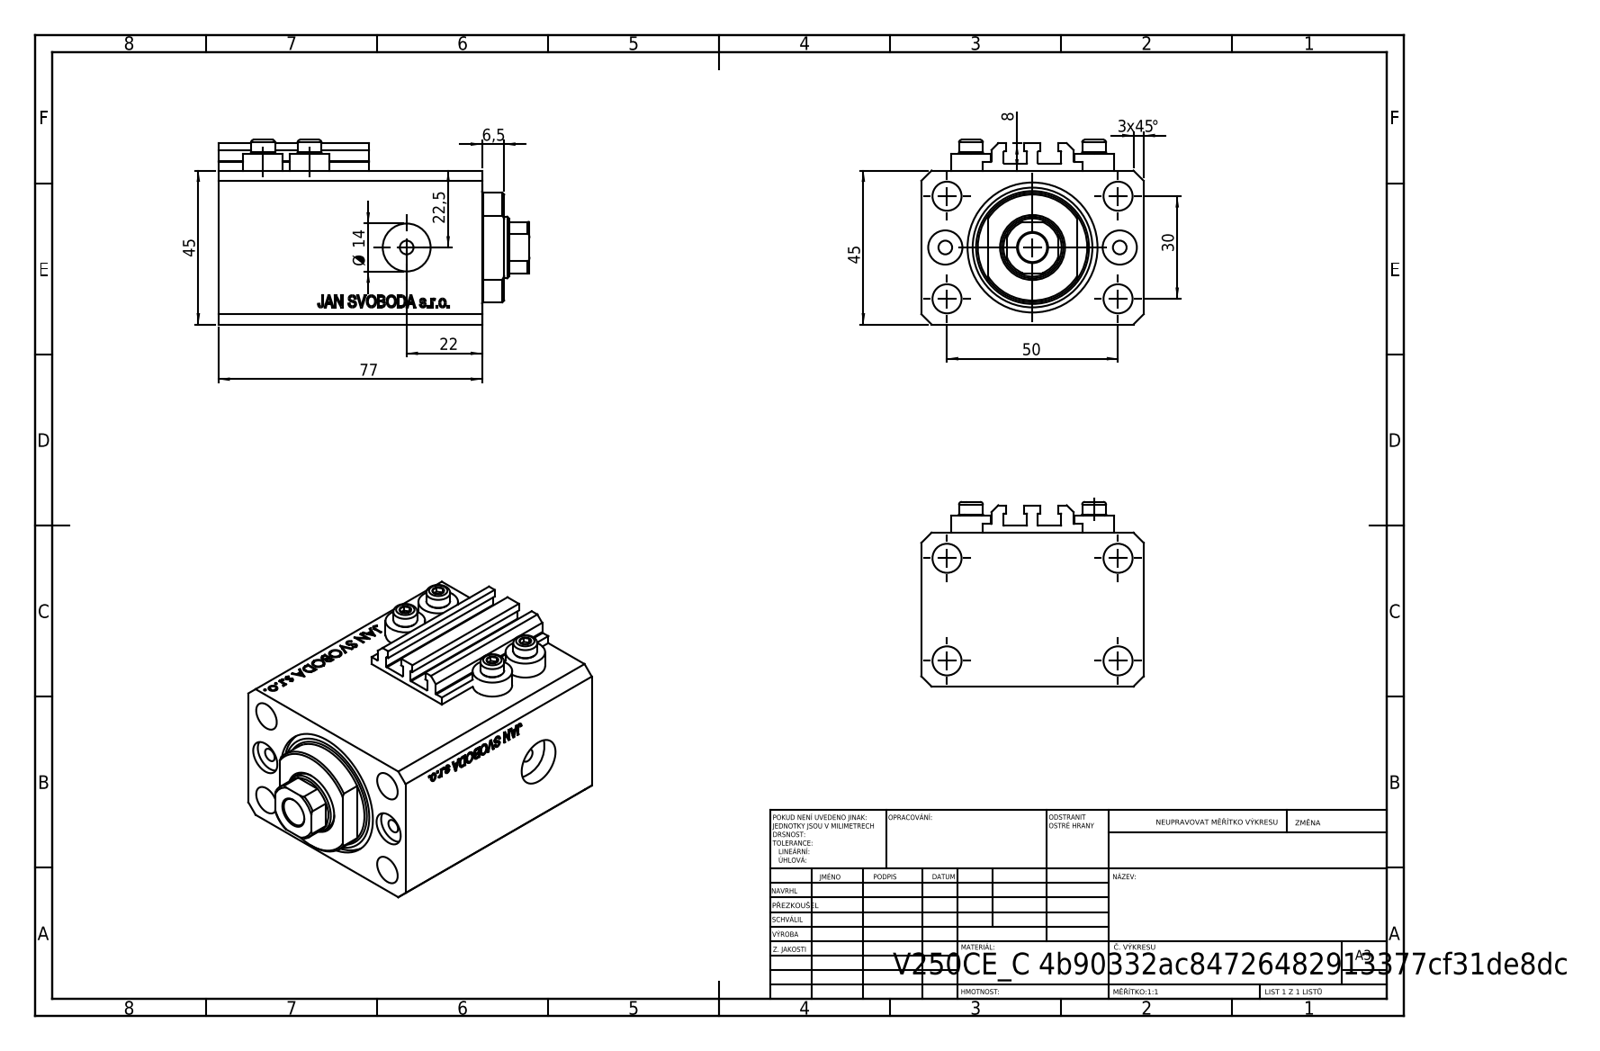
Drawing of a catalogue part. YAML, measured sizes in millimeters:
part_name: "V250CE_C_VCP; ALLEN BOLT V250CE; V250CE_C; V250CE_VC_C"
step_written_by: "SolidWorks 2019 (CONFIG_CONTROL_DESIGN)"
units: millimeters
bodies: {solids: 8, faces: 1033, planar: 503, cylindrical: 86, other: 444}
overall_size: [90.9, 65, 54]
volume: 211888
surface_area: 59424
round_holes:
  - {diameter: 4, count: 8}
  - {diameter: 8.5, count: 5}
  - {diameter: 10, count: 2}
  - {diameter: 14, count: 2}
  - {diameter: 18, count: 1}
  - {diameter: 25, count: 1}
  - {diameter: 38, count: 1}
round_bosses_or_shafts:
  - {diameter: 11.6, count: 4}
  - {diameter: 7, count: 4}
partial_cylinders:
  - {radius: 0.2, count: 10}
  - {radius: 8.5, count: 1}
  - {radius: 16, count: 1}
face_to_face_distances: [45, 65, 51.9, 77, 25.1, 6.9, 70.1, 3, 47, 10]
hole_center_spacings: [15.01, 29.15, 52.68, 13.6, 25.5, 30, 36, 38.48]
